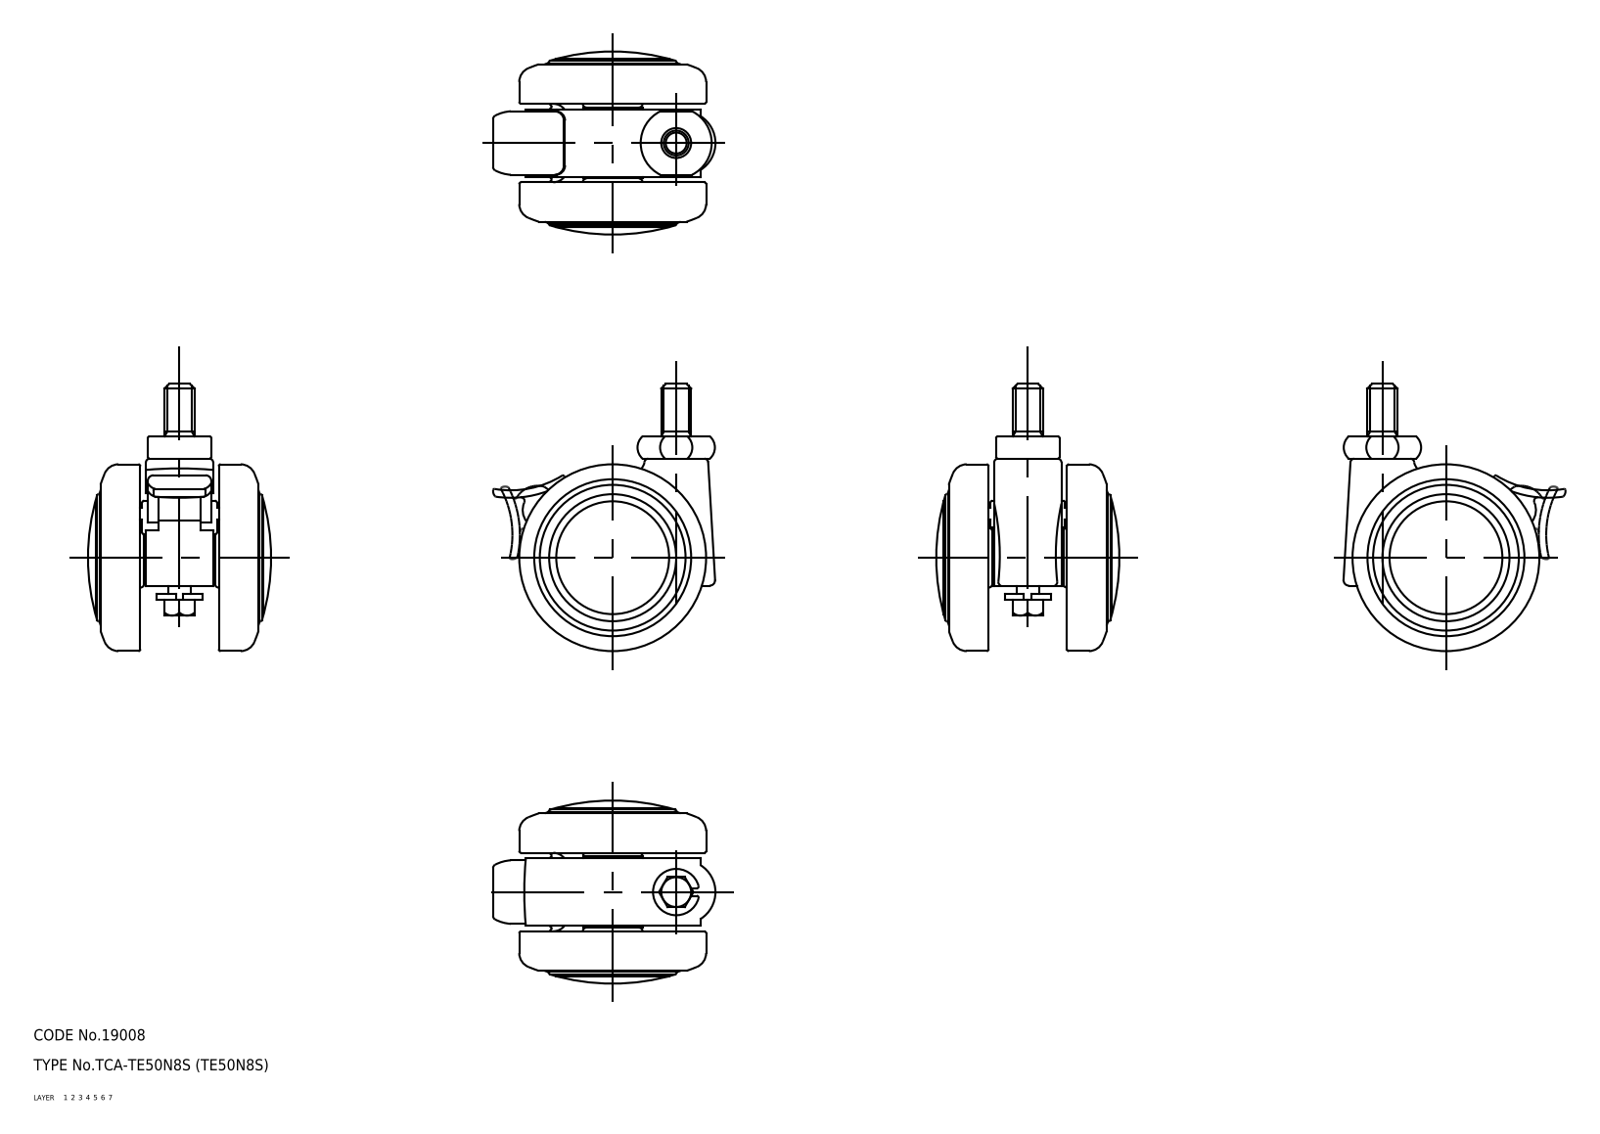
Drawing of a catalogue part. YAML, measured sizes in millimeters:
part_name: "wheel; main shaft; lever; TE50N8S_3585_36"
step_written_by: "CADfix (AUTOMOTIVE_DESIGN)"
units: millimeters
bodies: {solids: 5, faces: 231, planar: 0, cylindrical: 0, other: 231}
overall_size: [71.5, 59.42, 49]
volume: 62889
surface_area: 27454
